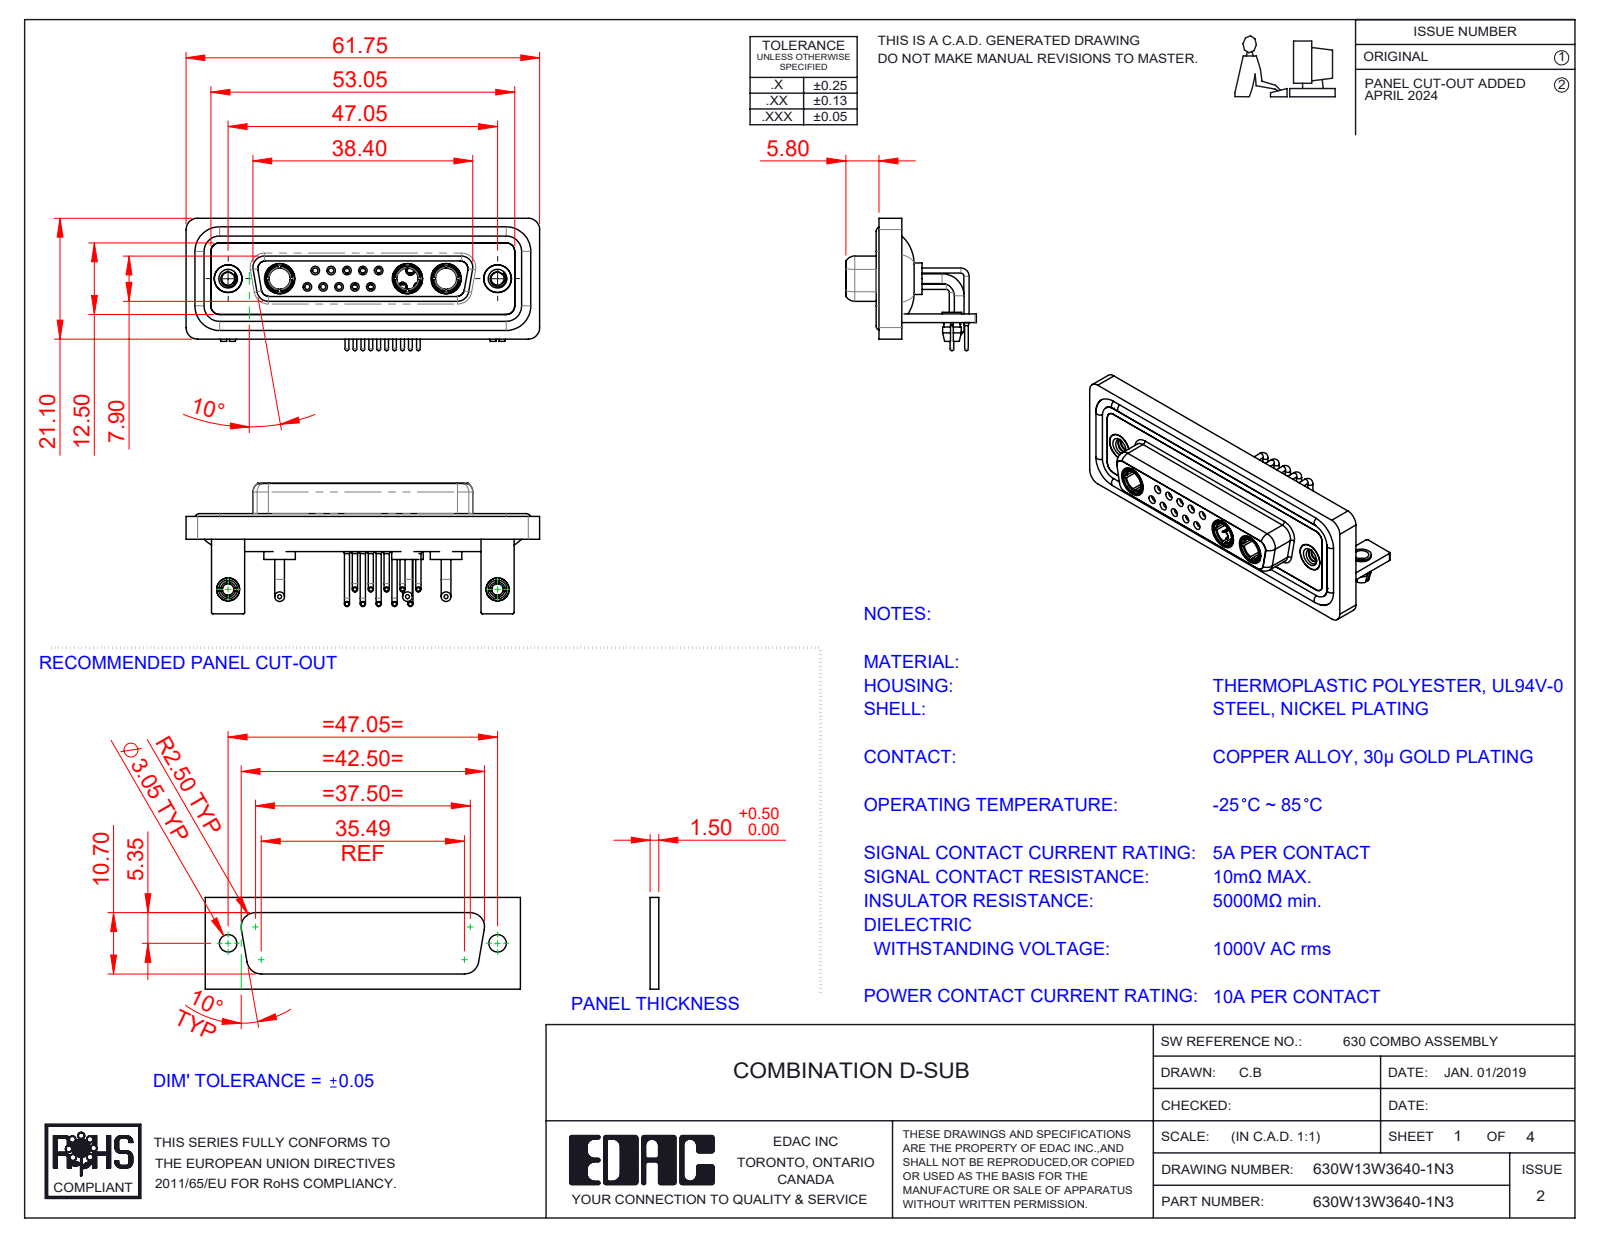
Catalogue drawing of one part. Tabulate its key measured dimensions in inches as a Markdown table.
| quantity | value |
| --- | --- |
| part name | 630Combo Board Lock_50 Contacts; Power Socket_10A RA; 630Combo Contact Row 2_50 Contacts; 630Combo Contact Row 1_50 Contacts (+7 more) |
| STEP written by | SolidWorks 2023 (CONFIG_CONTROL_DESIGN) |
| units | inches |
| bodies | 27 solids, 1290 faces (410 planar, 549 cylindrical, 331 other) |
| overall size | 2.431 × 0.91 × 0.898 |
| volume | 0.531 in³ |
| surface area | 23.39 in² |
| round holes (diameter × count) | 0.079 × 12, 0.035 × 10, 0.043 × 10, 0.059 × 10, 0.063 × 5, 0.067 × 5, 0.191 × 5, 0.146 × 3, 0.209 × 3, 0.089 × 2, 0.098 × 2, 0.126 × 2 |
| round bosses / shafts (diameter × count) | 0.035 × 15, 0.063 × 12, 0.026 × 10, 0.067 × 6, 0.079 × 5, 0.059 × 5, 0.217 × 3, 0.205 × 3 |
| partial cylindrical surfaces (radius × count) | 0.079 × 19, 0.059 × 18, 0.01 × 16, 0.053 × 8, 0.063 × 8, 0.02 × 5, 0.024 × 4, 0.026 × 4 |
| main face-to-face distances | 0.016, 0.071, 0.114, 0.059, 0.146, 0.161, 0.043, 0.055, 0.063, 0.122 |
| hole center spacings | 0.124, 0.109, 0.218, 0.198, 0.327, 0.198, 0.295, 0.436 |
